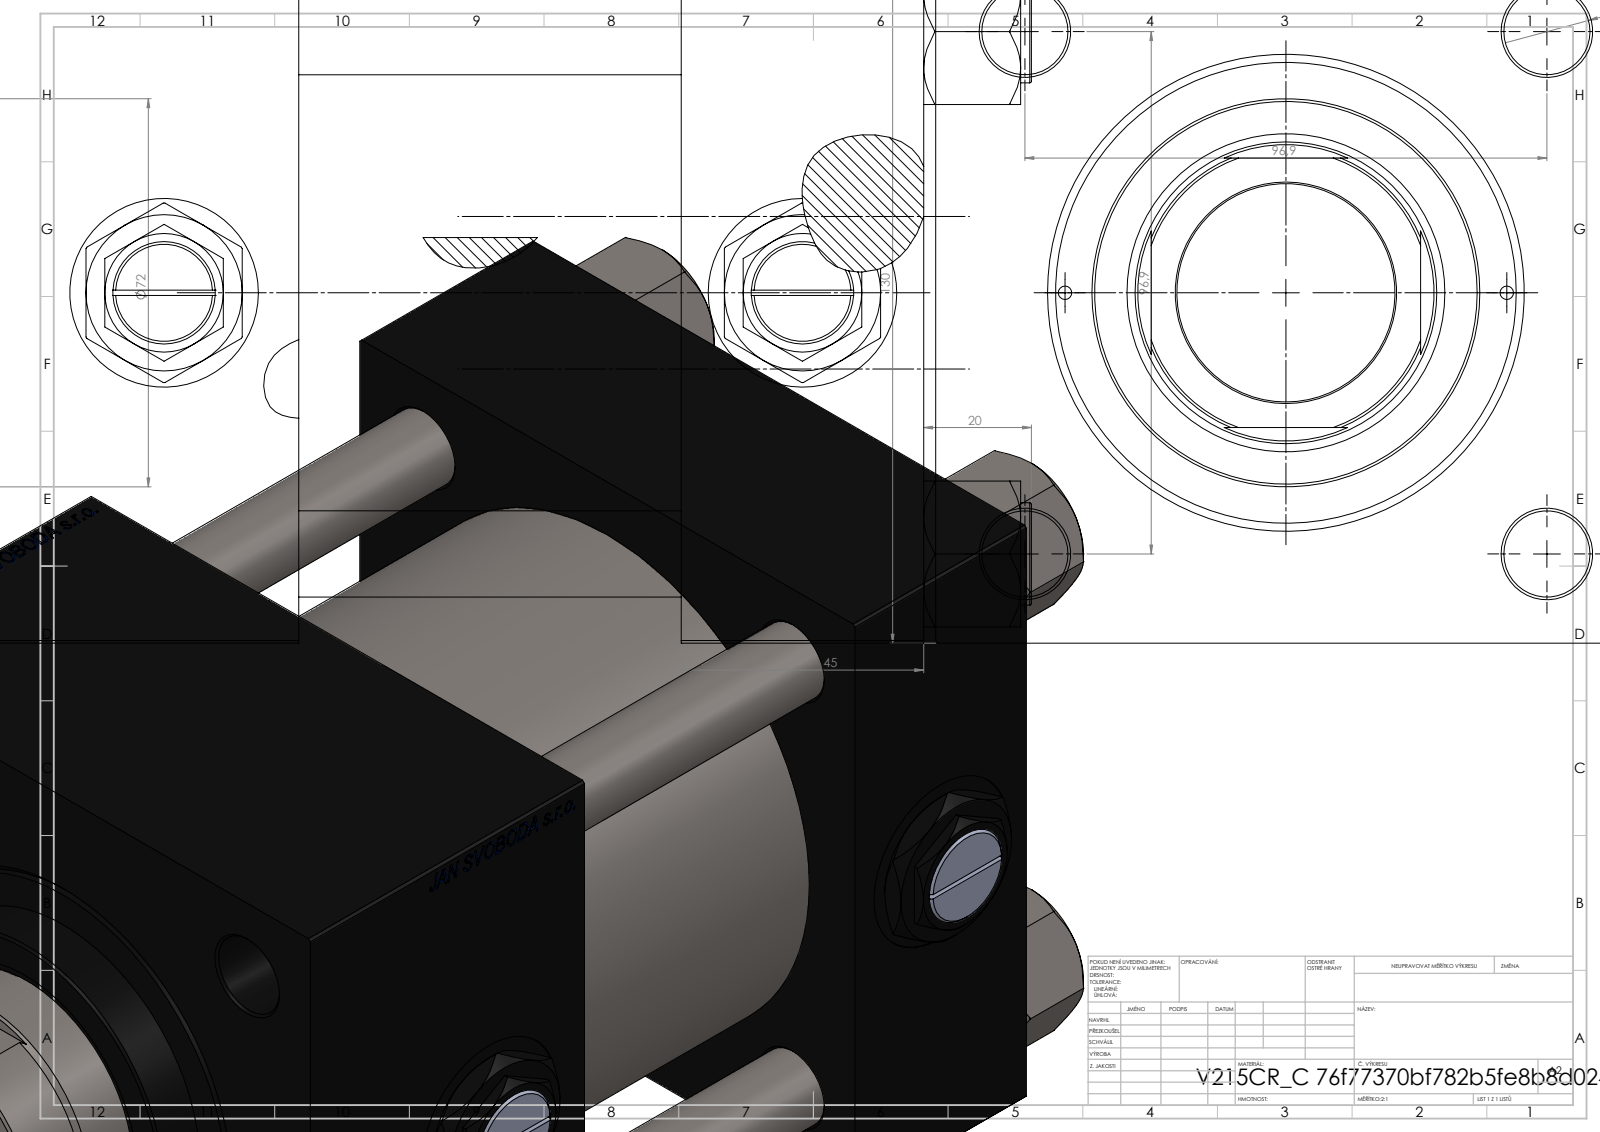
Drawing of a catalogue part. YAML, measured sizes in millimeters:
part_name: "Zatka_pro_OIL_PORT; V215CR_VCP_C; V215_VC_A; V215CR_C_TYCINKA (+2 more)"
step_written_by: "SolidWorks 2019 (CONFIG_CONTROL_DESIGN)"
units: millimeters
bodies: {solids: 13, faces: 1303, planar: 623, cylindrical: 102, other: 578}
overall_size: [243, 137, 130]
volume: 2461000
surface_area: 340510
round_holes:
  - {diameter: 16, count: 4}
  - {diameter: 2.5, count: 2}
  - {diameter: 7, count: 2}
  - {diameter: 26.44, count: 2}
  - {diameter: 35, count: 2}
  - {diameter: 40.5, count: 1}
  - {diameter: 56, count: 1}
  - {diameter: 59, count: 1}
  - {diameter: 76, count: 1}
  - {diameter: 85.5, count: 1}
  - {diameter: 100, count: 1}
round_bosses_or_shafts:
  - {diameter: 19, count: 4}
  - {diameter: 106, count: 1}
  - {diameter: 72, count: 1}
partial_cylinders:
  - {radius: 27, count: 1}
face_to_face_distances: [130, 45, 188, 143, 116, 71, 72, 20, 51, 92]
hole_center_spacings: [49.02, 68.52, 96.9, 101.73, 41, 137.04, 82, 118.5]
